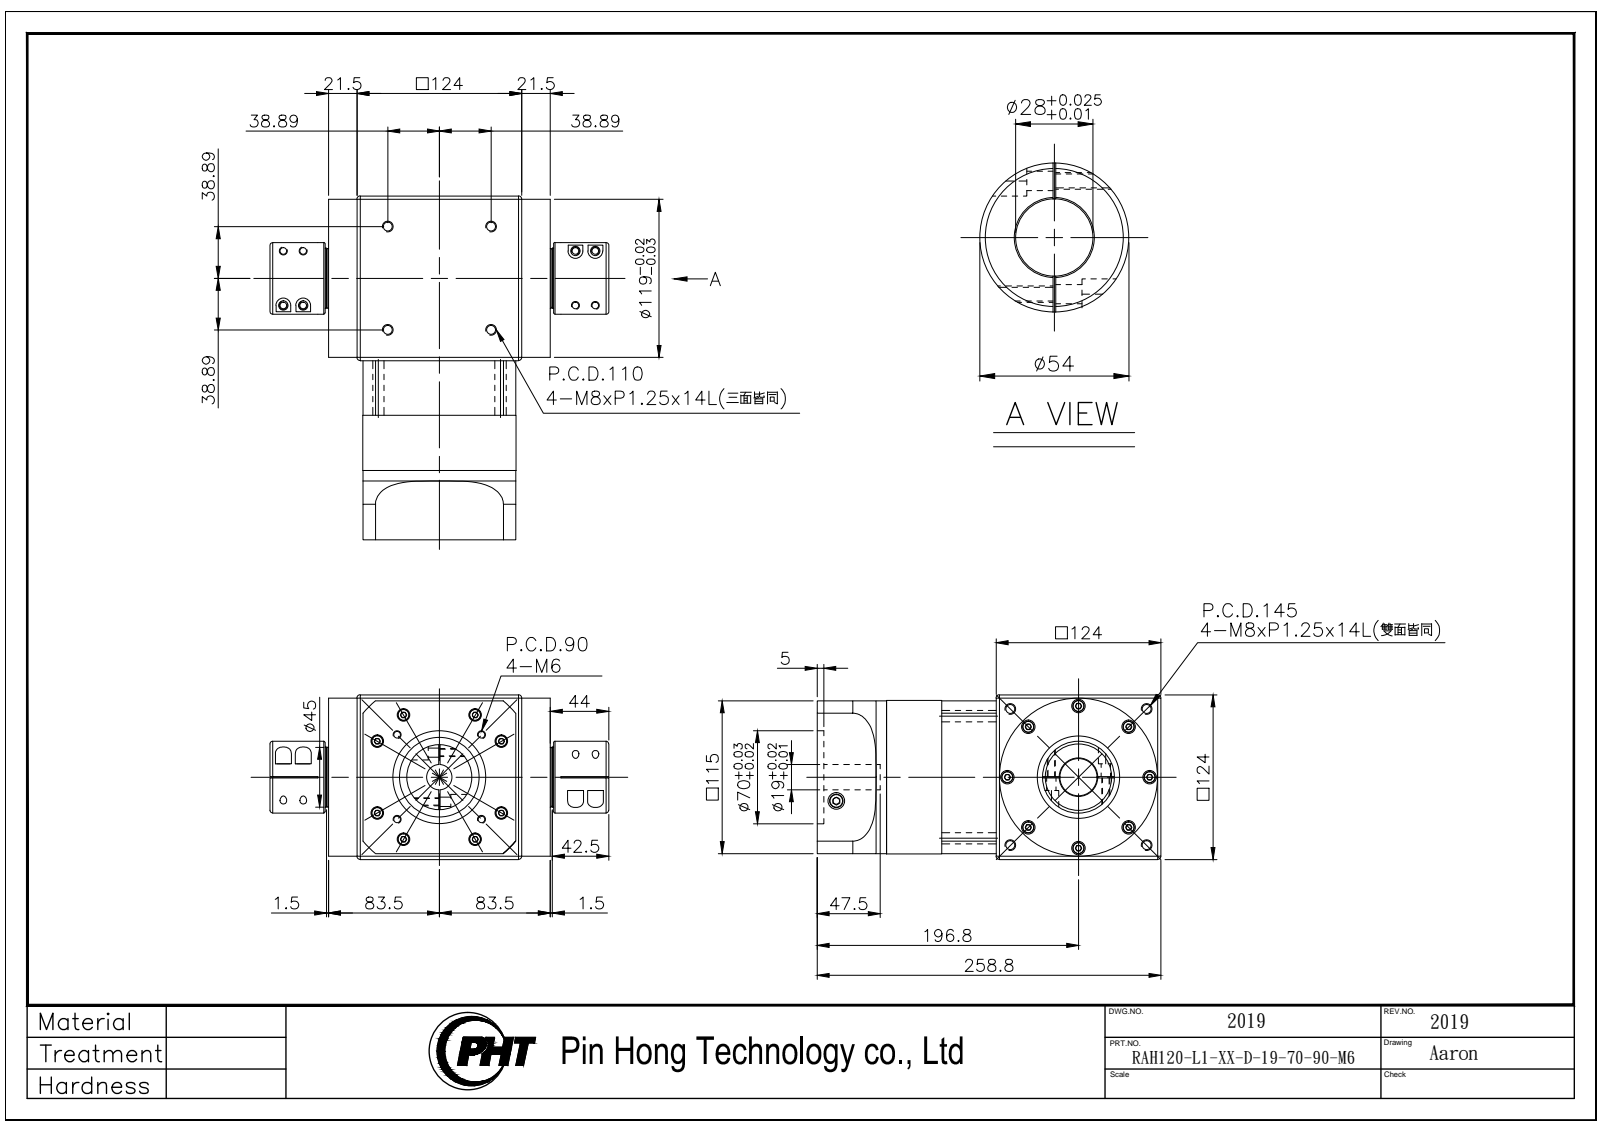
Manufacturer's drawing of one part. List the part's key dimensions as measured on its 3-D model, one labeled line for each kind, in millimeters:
Part name (STEP PRODUCT): RAH120-L1-XX-D-19-70-90-M6_2019
STEP written by: SolidWorks 2016 (AUTOMOTIVE_DESIGN)
Units: millimetres
Bodies: 2 solids, 1264 faces (656 planar, 384 cylindrical, 224 other)
Overall size (bounding box): 258.8 × 255 × 124
Volume: 3 876 000 mm³ · Surface area: 317 816 mm²
Round holes (diameter × count): ⌀6.8 ×12, ⌀5.4 ×8, ⌀7 ×8, ⌀9 ×8, ⌀9.5 ×8, ⌀14 ×8, ⌀5 ×4, ⌀8.5 ×4, ⌀12.7 ×2, ⌀19 ×1, ⌀28 ×1, ⌀32 ×1
Round bosses / shafts (diameter × count): ⌀13 ×12, ⌀10.5 ×8, ⌀10 ×8, ⌀8.5 ×8, ⌀6 ×8, ⌀119 ×1, ⌀115.5 ×1, ⌀115 ×1
Partial cylindrical surfaces — rounded edges, fillets, slot ends (radius × count): R3.52 ×8, R5.5 ×8, R75 ×1, R86.2 ×1
Main face-to-face distances: 124, 4.5, 119.5, 115, 26, 141, 3, 121, 134.8, 137.8
Hole centre spacings: 54, 10, 14.26, 15.71, 18.98, 39.8, 51.28, 52
